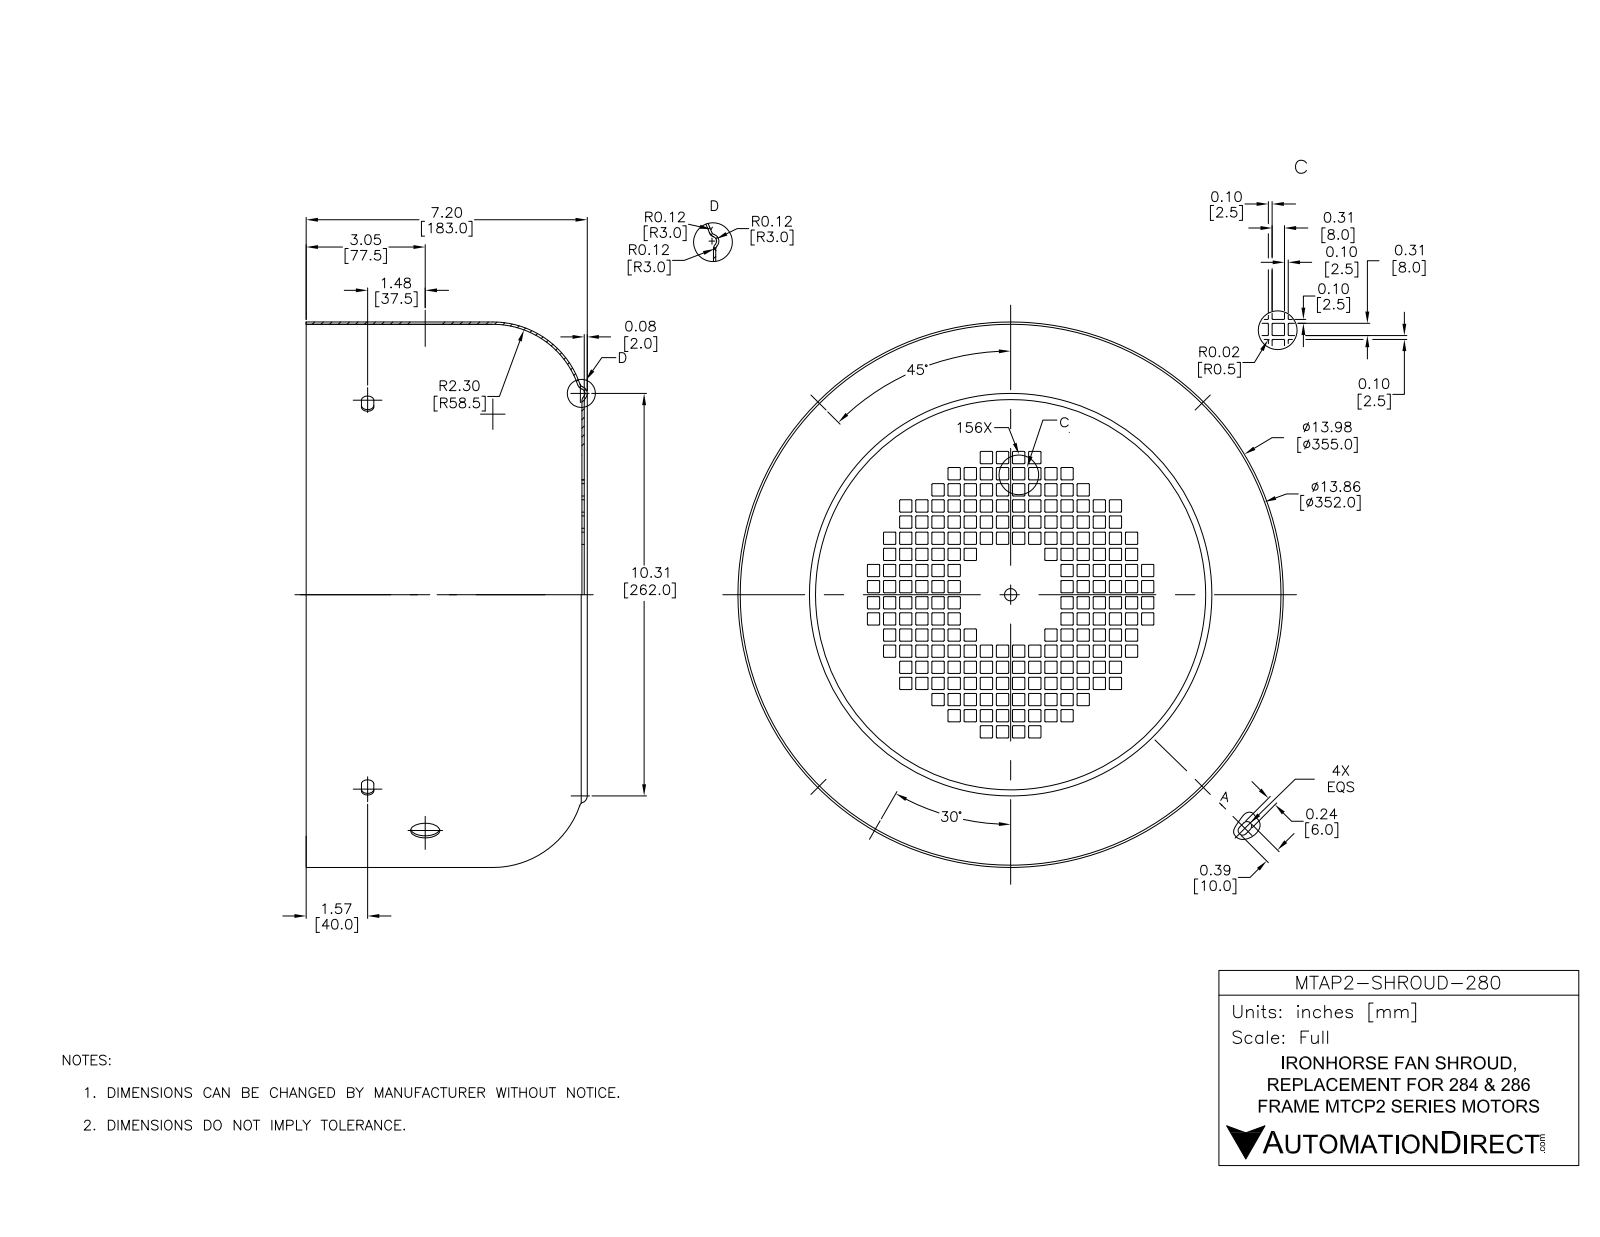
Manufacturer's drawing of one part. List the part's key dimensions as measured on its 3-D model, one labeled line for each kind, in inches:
Part name (STEP PRODUCT): MTAP2-SHROUD-280
STEP written by: SolidWorks 2017 (AUTOMOTIVE_DESIGN)
Units: inches
Bodies: 1 solid, 1046 faces (1024 planar, 6 cylindrical, 16 other)
Overall size (bounding box): 13.976 × 13.976 × 7.205
Volume: 24.4 in³ · Surface area: 847.6 in²
Round holes (diameter × count): ⌀0.315 ×1, ⌀13.858 ×1
Round bosses / shafts (diameter × count): ⌀13.976 ×1
Main face-to-face distances: 0.059, 0.039, 0.02, 7.067, 7.106, 7.126, 0.413, 0.827, 1.24, 0.315
